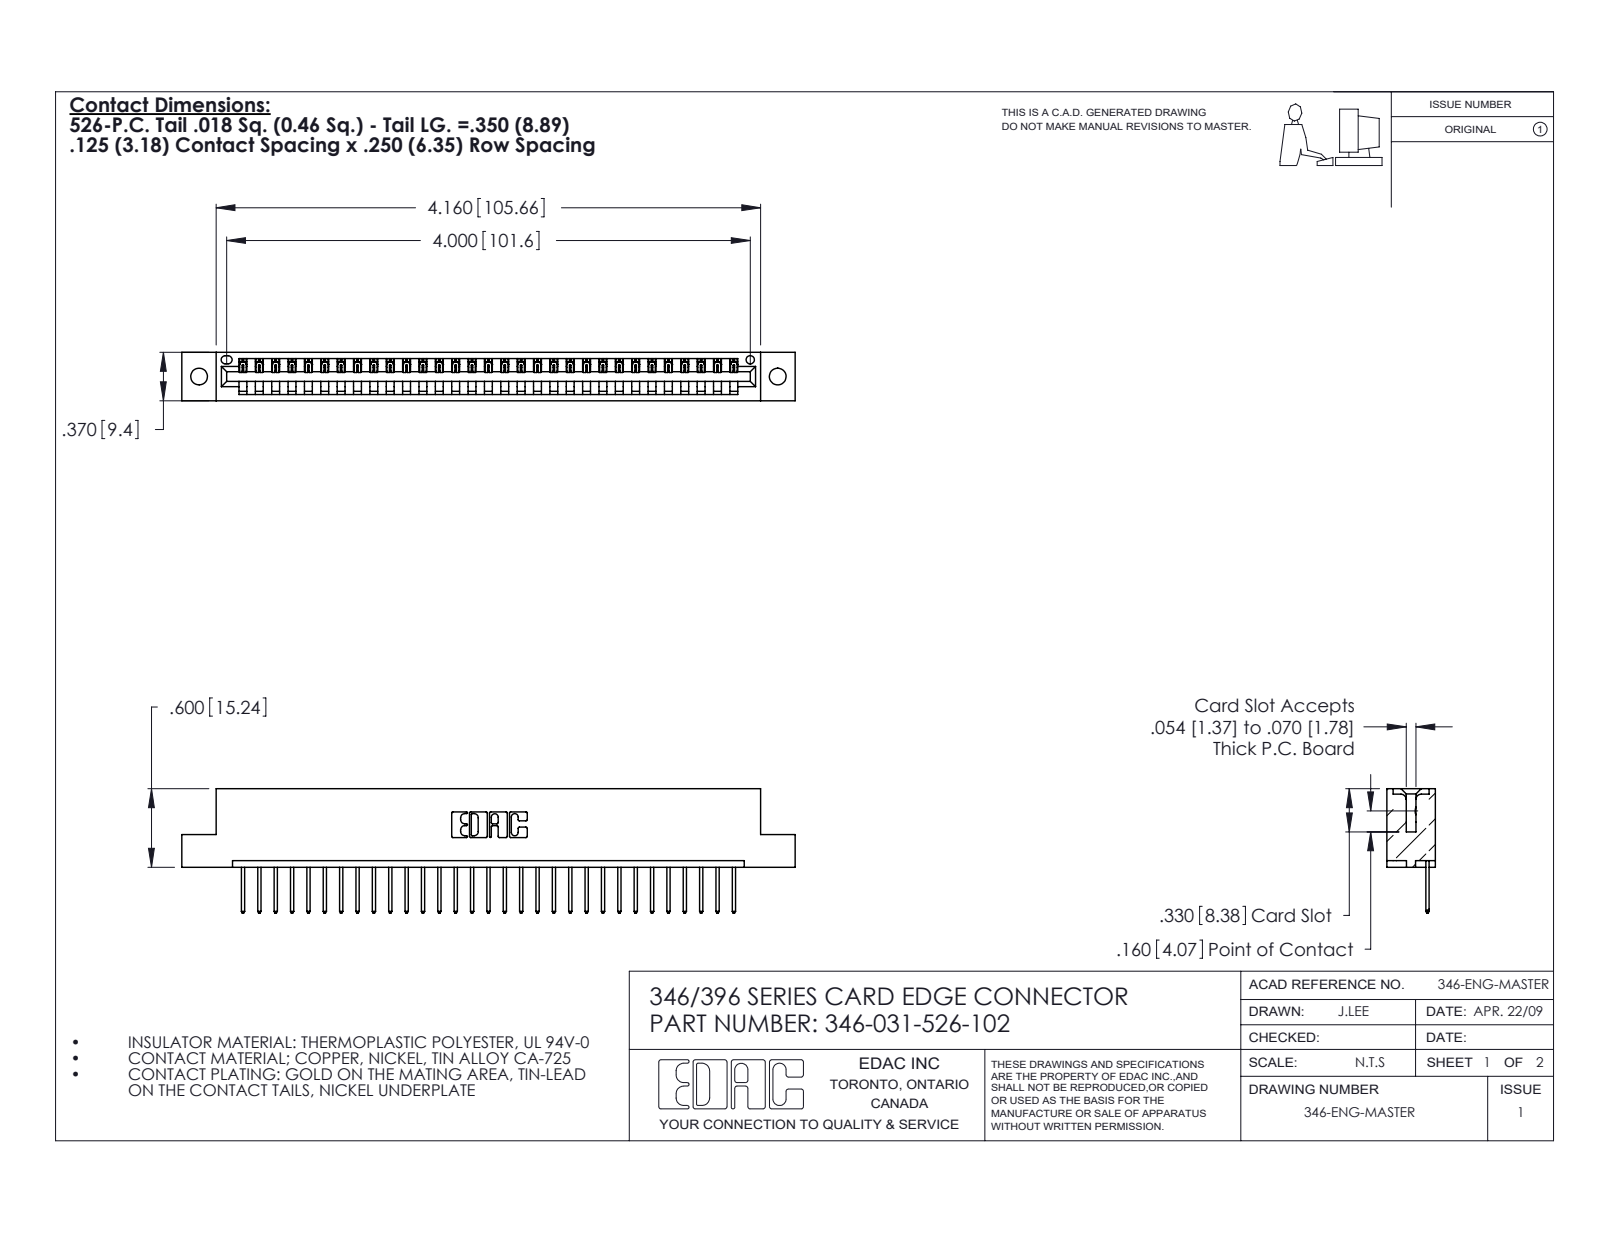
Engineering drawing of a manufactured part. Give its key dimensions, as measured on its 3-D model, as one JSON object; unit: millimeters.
{"part_name": "345-292-001_345-293-126; 346 Part_Flush Mounting Lugs - 0.128 Dia; 346-031-526-102", "step_written_by": "SolidWorks 2020 (CONFIG_CONTROL_DESIGN)", "units": "millimeters", "bodies": {"solids": 32, "faces": 1920, "planar": 1316, "cylindrical": 604, "other": 0}, "overall_size": [119, 24.1, 9.4], "volume_mm3": 11300, "surface_area_mm2": 13650, "round_holes": [[3.3, 2], [1.6, 1]], "partial_cylinders_radius": [[0.2, 62], [0.3, 62], [0.3, 22], [0.2, 6], [0.8, 6], [0.7, 3], [0.8, 2], [1, 2]], "face_to_face_distances": [1.2, 8.2, 9.4, 6.4, 1.8, 7.6, 0.6, 3.8, 5.6, 2.5], "hole_center_spacings": [6.2, 107, 112.3]}
